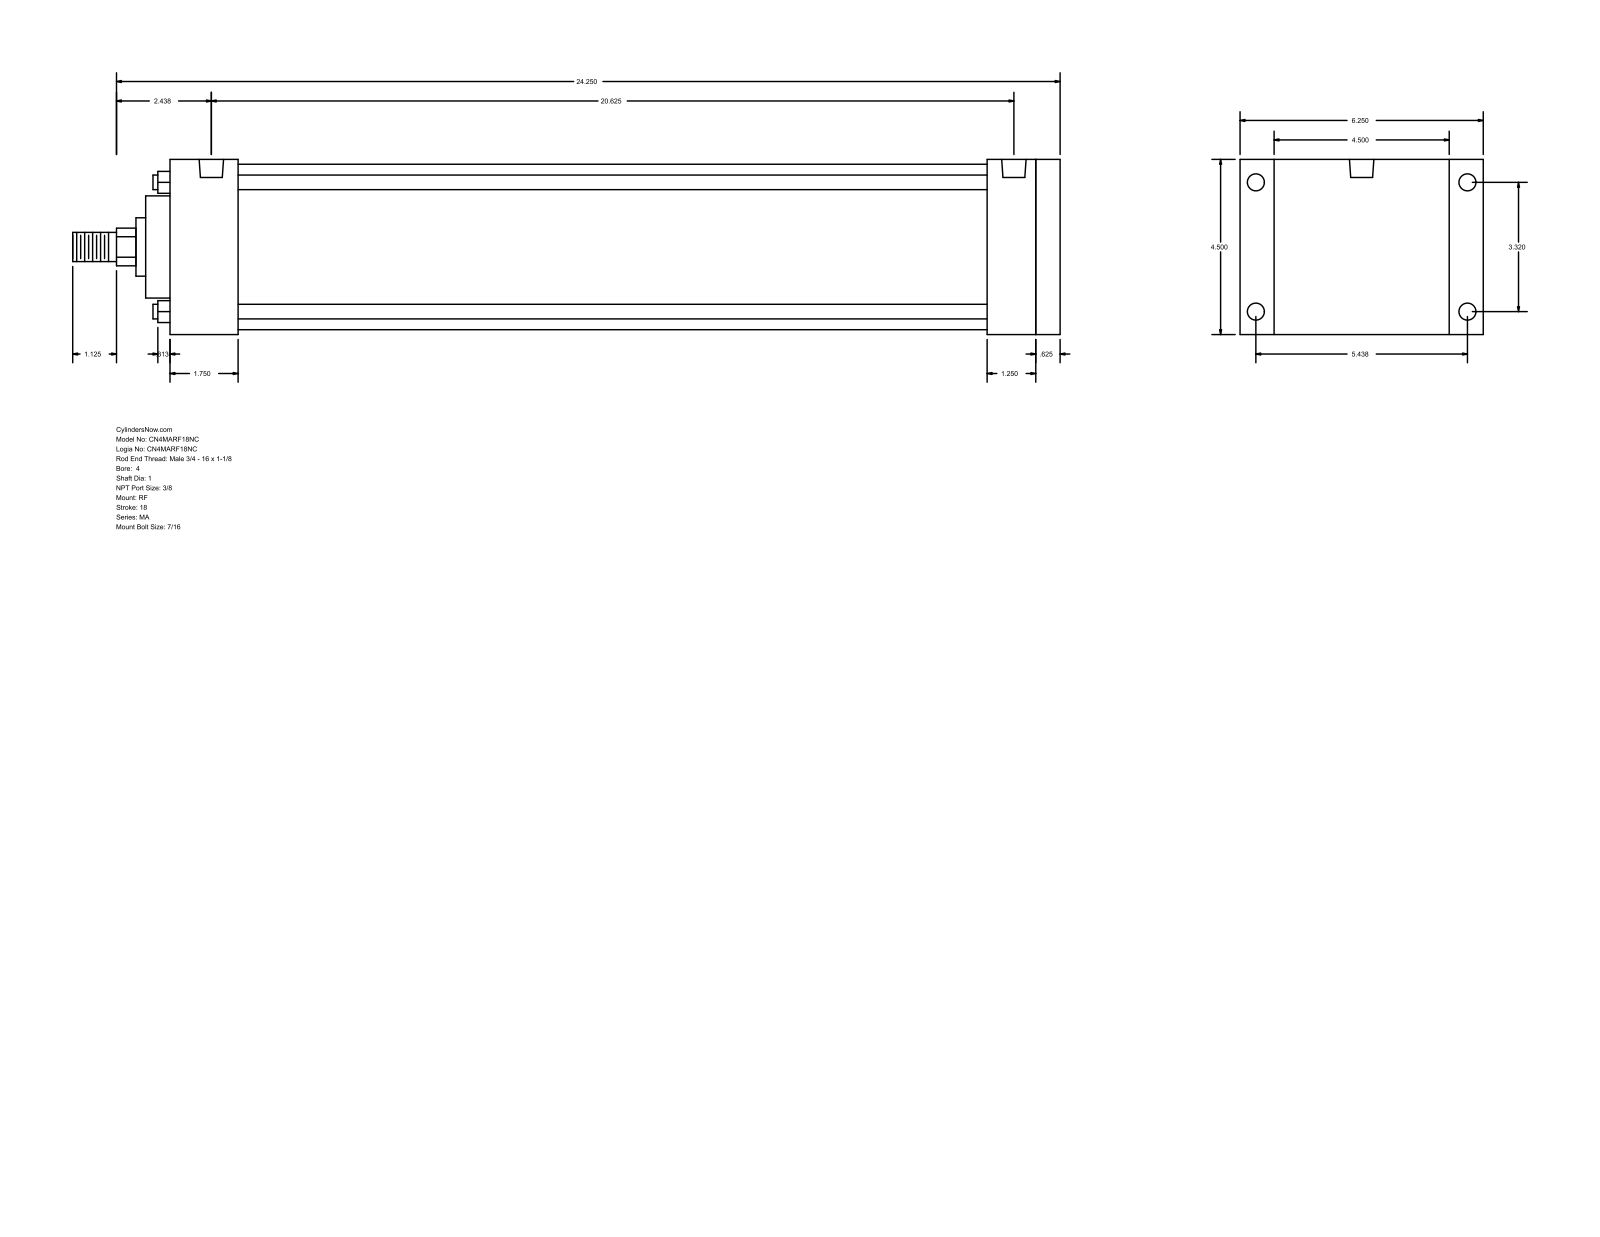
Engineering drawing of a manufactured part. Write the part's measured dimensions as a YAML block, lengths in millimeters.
part_name: "MA_RF__0400_1"
step_written_by: "GSSL Pune (CONFIG_CONTROL_DESIGN)"
units: millimeters
bodies: {solids: 0, faces: 94, planar: 65, cylindrical: 29, other: 0}
overall_size: [644.52, 158.75, 114.3]
round_holes:
  - {diameter: 11.11, count: 8}
  - {diameter: 15.93, count: 2}
round_bosses_or_shafts:
  - {diameter: 9.53, count: 4}
  - {diameter: 107.95, count: 1}
  - {diameter: 66.67, count: 1}
  - {diameter: 38.1, count: 1}
  - {diameter: 25.4, count: 1}
  - {diameter: 19.05, count: 1}
partial_cylinders:
  - {radius: 12.29, count: 1}
face_to_face_distances: [114.3, 581.03, 15.87, 565.16, 47.62, 22.23, 136.53, 533.41, 31.75, 44.46]
hole_center_spacings: [84.32, 138.12, 161.82, 514.35, 4.76, 4.77, 519.11, 519.12]
